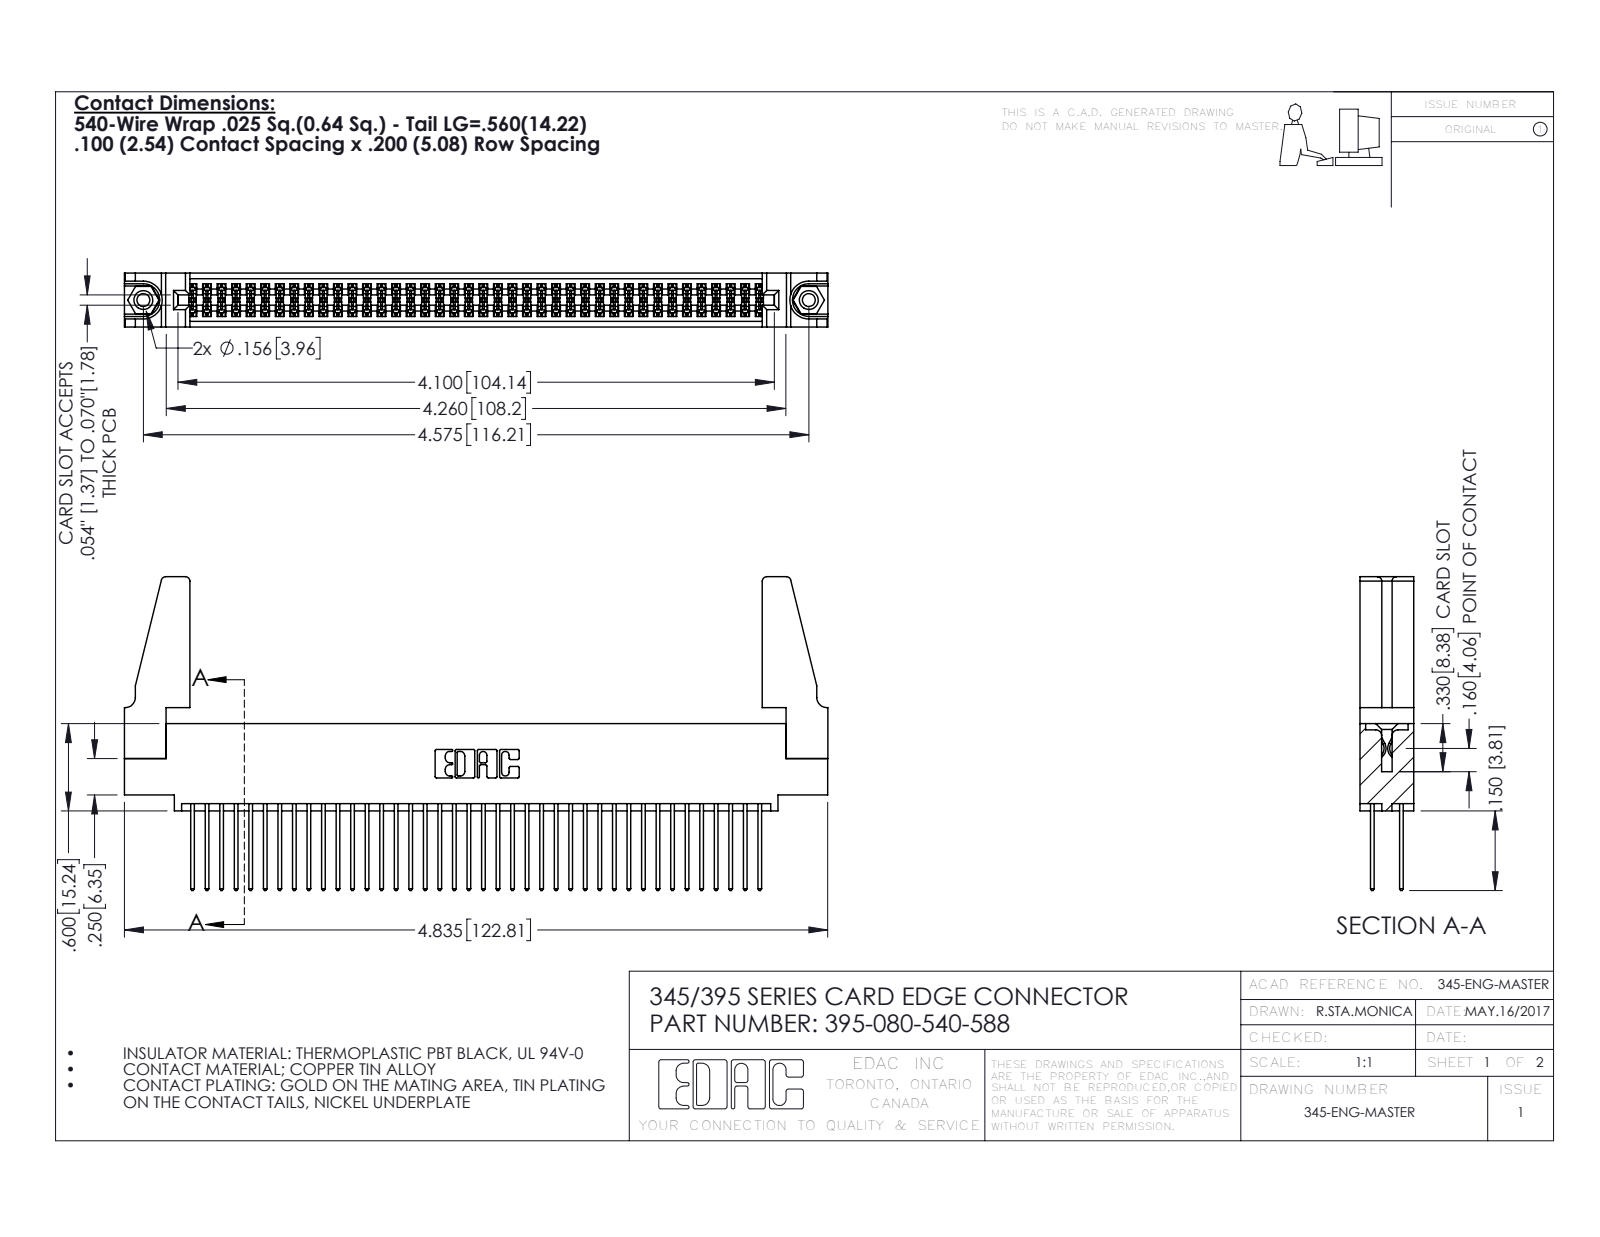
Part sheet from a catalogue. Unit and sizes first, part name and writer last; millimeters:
Units: millimetres
Overall size (bounding box): 122.8 × 54.8 × 9.4
Round holes (diameter × count): ⌀2.3 ×2, ⌀3.2 ×2, ⌀4 ×2, ⌀1.6 ×1
Round bosses / shafts (diameter × count): ⌀3.9 ×2
Partial cylindrical surfaces — rounded edges, fillets, slot ends (radius × count): R0.2 ×120, R0.3 ×80, R0.3 ×22, R0.8 ×8, R0.2 ×6, R0.8 ×6, R0.7 ×3, R0.4 ×2
Main face-to-face distances: 1.8, 7.6, 5.1, 2.5, 6.9, 0.6, 9.4, 5.7, 4.4, 3.8
Hole centre spacings: 6.9, 110.2, 116.2
Volume: 15 400 mm³ · Surface area: 22 540 mm²
Bodies: 85 solids, 4254 faces (2796 planar, 1442 cylindrical, 16 other)
Part name (STEP PRODUCT): 395-080-540-588; 345-292-001_345-293-140; 345-220-078_345-220-088; 345 Part_0.110 Offset - 0.156 Dia-TH (+1 more)
STEP written by: SolidWorks 2016 (CONFIG_CONTROL_DESIGN)
